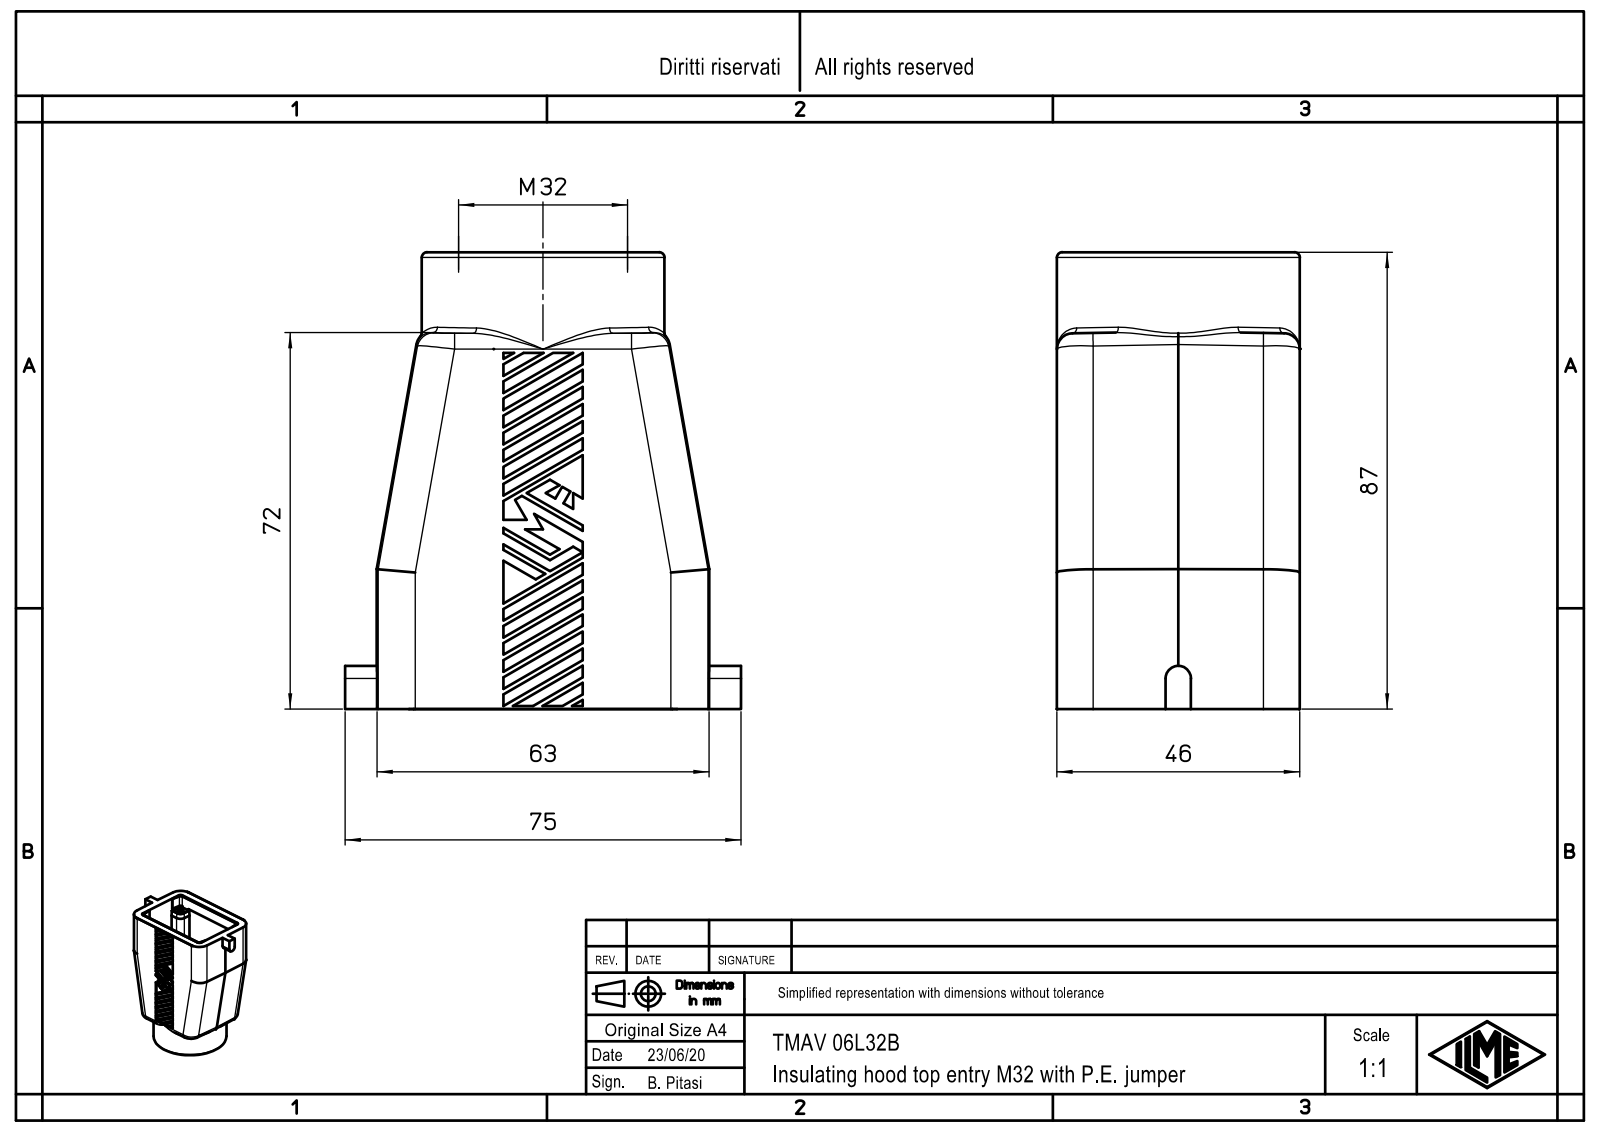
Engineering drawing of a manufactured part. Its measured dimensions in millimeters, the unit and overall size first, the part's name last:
Units: millimetres
Overall size (bounding box): 86.5 × 75 × 46
Round holes (diameter × count): ⌀3 ×4, ⌀3.5 ×4, ⌀28 ×1, ⌀32 ×1
Round bosses / shafts (diameter × count): ⌀4.8 ×4, ⌀46 ×1
Partial cylindrical surfaces — rounded edges, fillets, slot ends (radius × count): R1.5 ×12, R7 ×8, R3 ×6, R1.3 ×4, R1.6 ×4, R2 ×4, R3.5 ×4, R2.4 ×1
Main face-to-face distances: 46, 45.5, 0.5, 63, 5.6, 86.5, 45, 5.3, 5.8, 40.2
Hole centre spacings: 25.81, 27, 44, 51.62
Volume: 96 369 mm³ · Surface area: 35 883 mm²
Bodies: 1 solid, 570 faces (400 planar, 80 cylindrical, 90 other)
Part name (STEP PRODUCT): TMAV_06L32B
STEP written by: Creo Elements/Direct Modeling 20.1B 02-Apr-2019 (C) Parametric Technology GmbH (AUTOMOTIVE_DESIGN)
